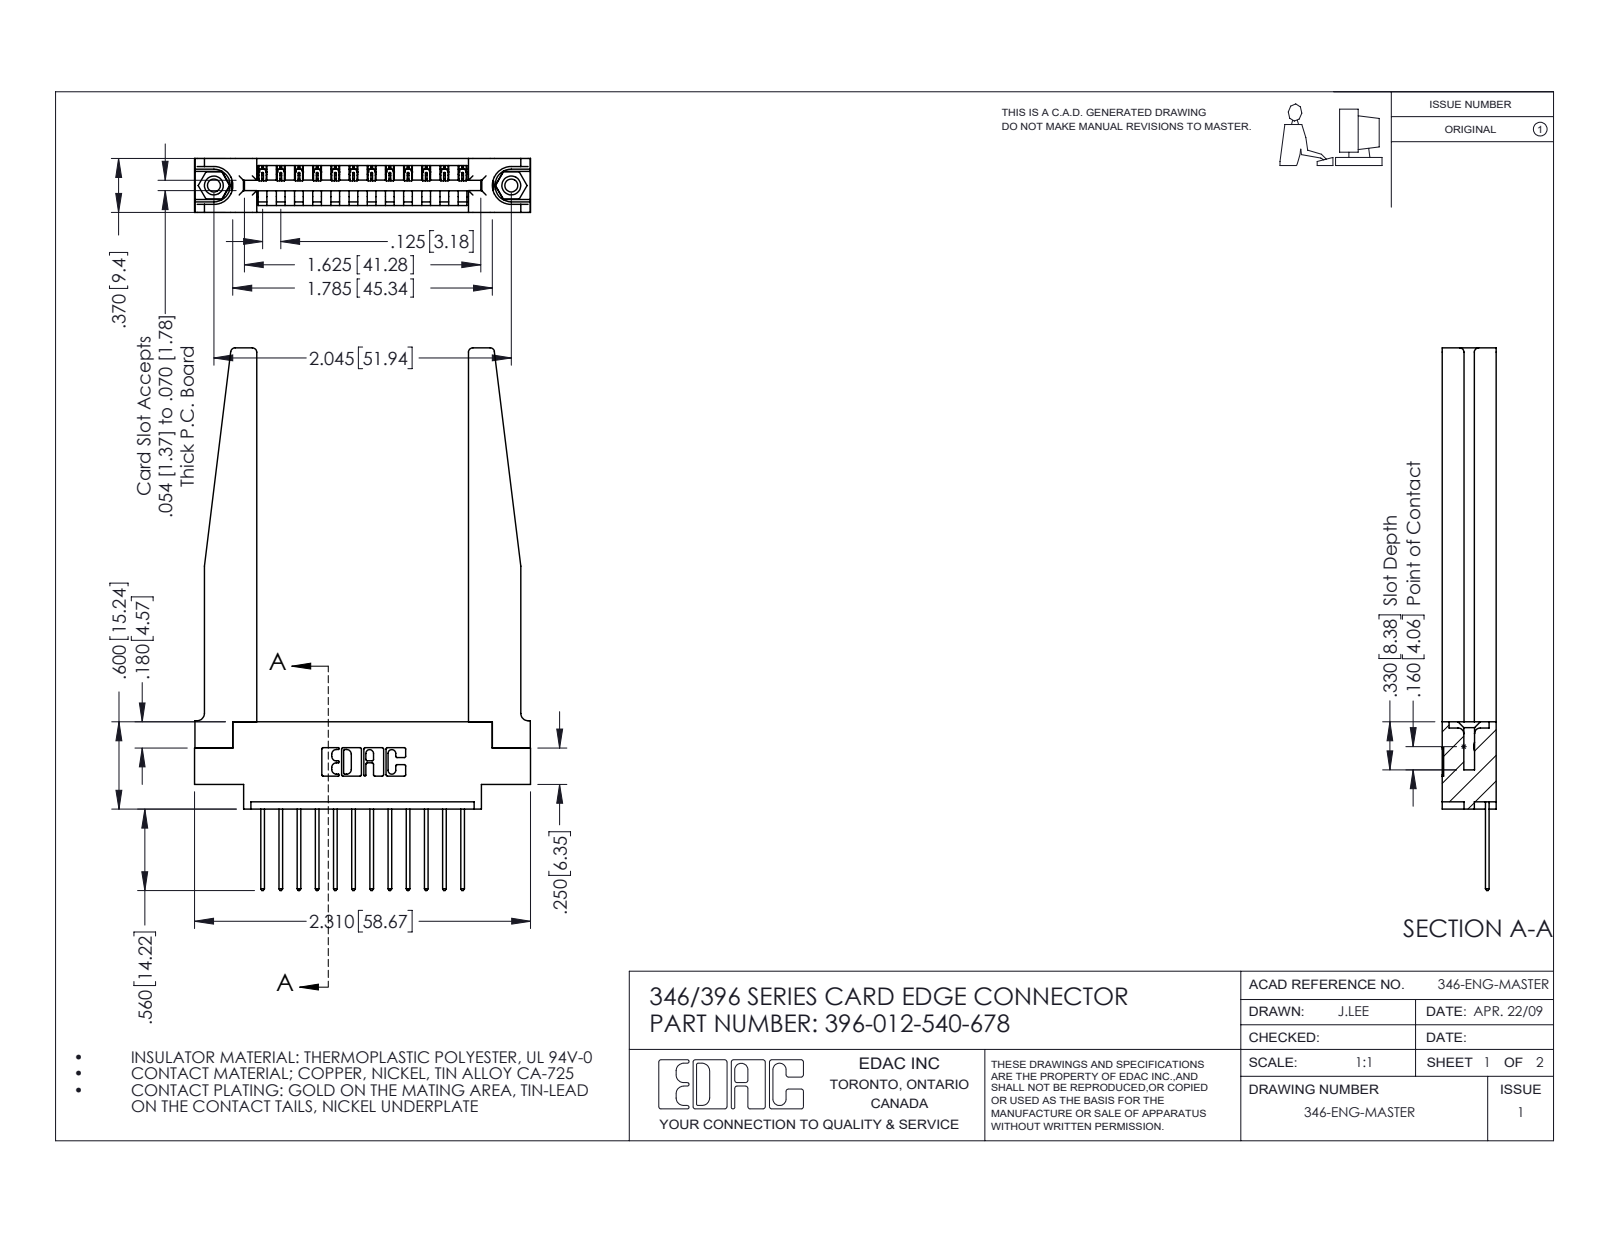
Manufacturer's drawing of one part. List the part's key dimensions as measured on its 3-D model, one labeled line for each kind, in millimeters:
Part name (STEP PRODUCT): 345-250-001_345-250-001-102; 396-012-540-678; 345-292-001_345-293-140; 346 Part_0.170 Offset - 0.156 Dia-TH (+1 more)
STEP written by: SolidWorks 2016 (CONFIG_CONTROL_DESIGN)
Units: millimetres
Bodies: 17 solids, 1056 faces (702 planar, 302 cylindrical, 52 other)
Overall size (bounding box): 94.7 × 58.7 × 9.4
Volume: 12 200 mm³ · Surface area: 13 080 mm²
Round holes (diameter × count): ⌀2.3 ×2, ⌀3.2 ×2, ⌀4 ×2, ⌀1.6 ×1
Round bosses / shafts (diameter × count): ⌀3.9 ×2
Partial cylindrical surfaces — rounded edges, fillets, slot ends (radius × count): R0.2 ×24, R0.3 ×24, R0.3 ×22, R0.8 ×8, R0.2 ×6, R0.8 ×6, R0.7 ×3, R0.8 ×2
Main face-to-face distances: 9.4, 3.8, 1.8, 3.8, 1.2, 8.2, 6.4, 5.6, 2.6, 4.4
Hole centre spacings: 6.2, 46.7, 51.9
